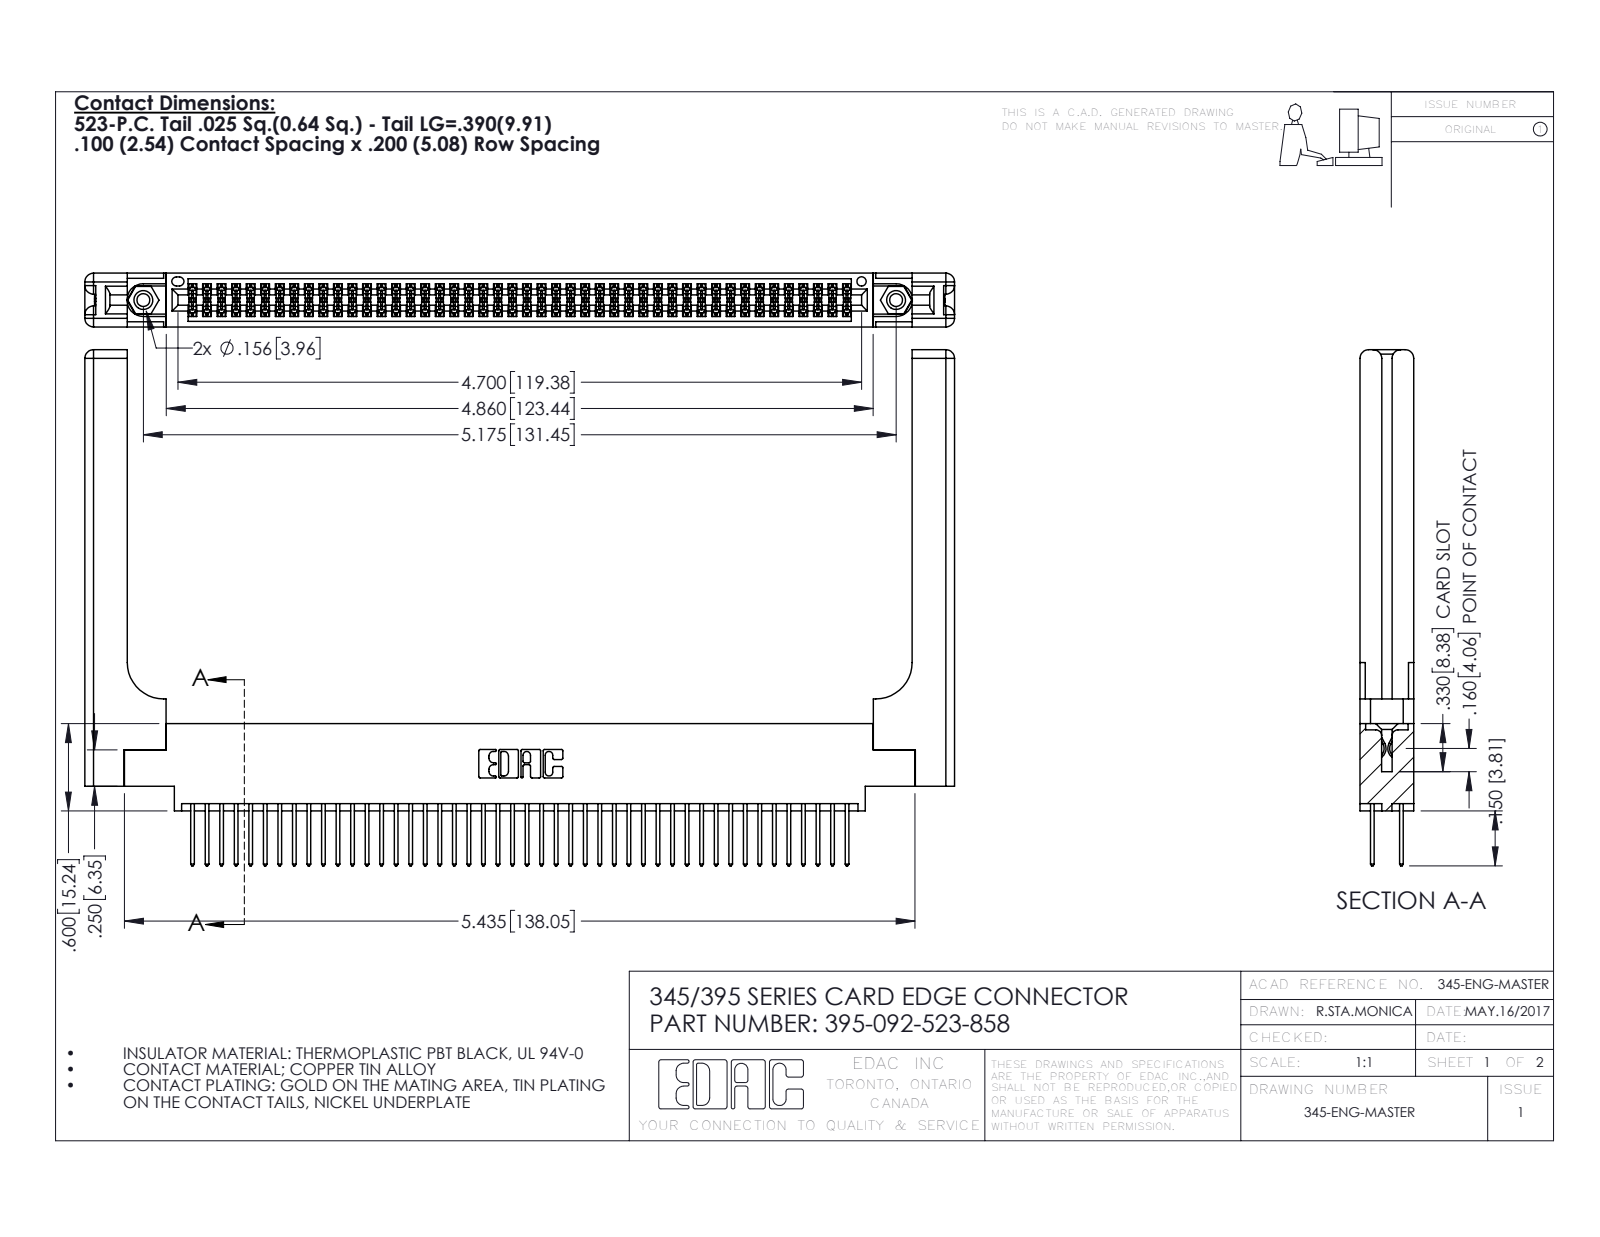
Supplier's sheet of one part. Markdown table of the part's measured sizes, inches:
| quantity | value |
| --- | --- |
| part name | 345-220-058_345-220-058; 345-250-001_345-250-001-102; 345-292-001_345-293-123; 395-092-523-858 (+1 more) |
| STEP written by | SolidWorks 2016 (CONFIG_CONTROL_DESIGN) |
| units | inches |
| bodies | 97 solids, 4986 faces (3268 planar, 1658 cylindrical, 60 other) |
| overall size | 5.979 × 3.547 × 0.37 |
| volume | 1.424 in³ |
| surface area | 43.55 in² |
| round holes (diameter × count) | 0.089 × 2, 0.125 × 2, 0.156 × 2, 0.064 × 1 |
| round bosses / shafts (diameter × count) | 0.155 × 2 |
| partial cylindrical surfaces (radius × count) | 0.006 × 138, 0.01 × 92, 0.01 × 22, 0.06 × 16, 0.007 × 6, 0.031 × 6, 0.026 × 3, 0.014 × 2 |
| main face-to-face distances | 0.072, 0.298, 0.37, 0.098, 0.272, 0.025, 0.2, 0.225, 0.175, 0.148 |
| hole center spacings | 0.27, 4.939, 5.175 |
